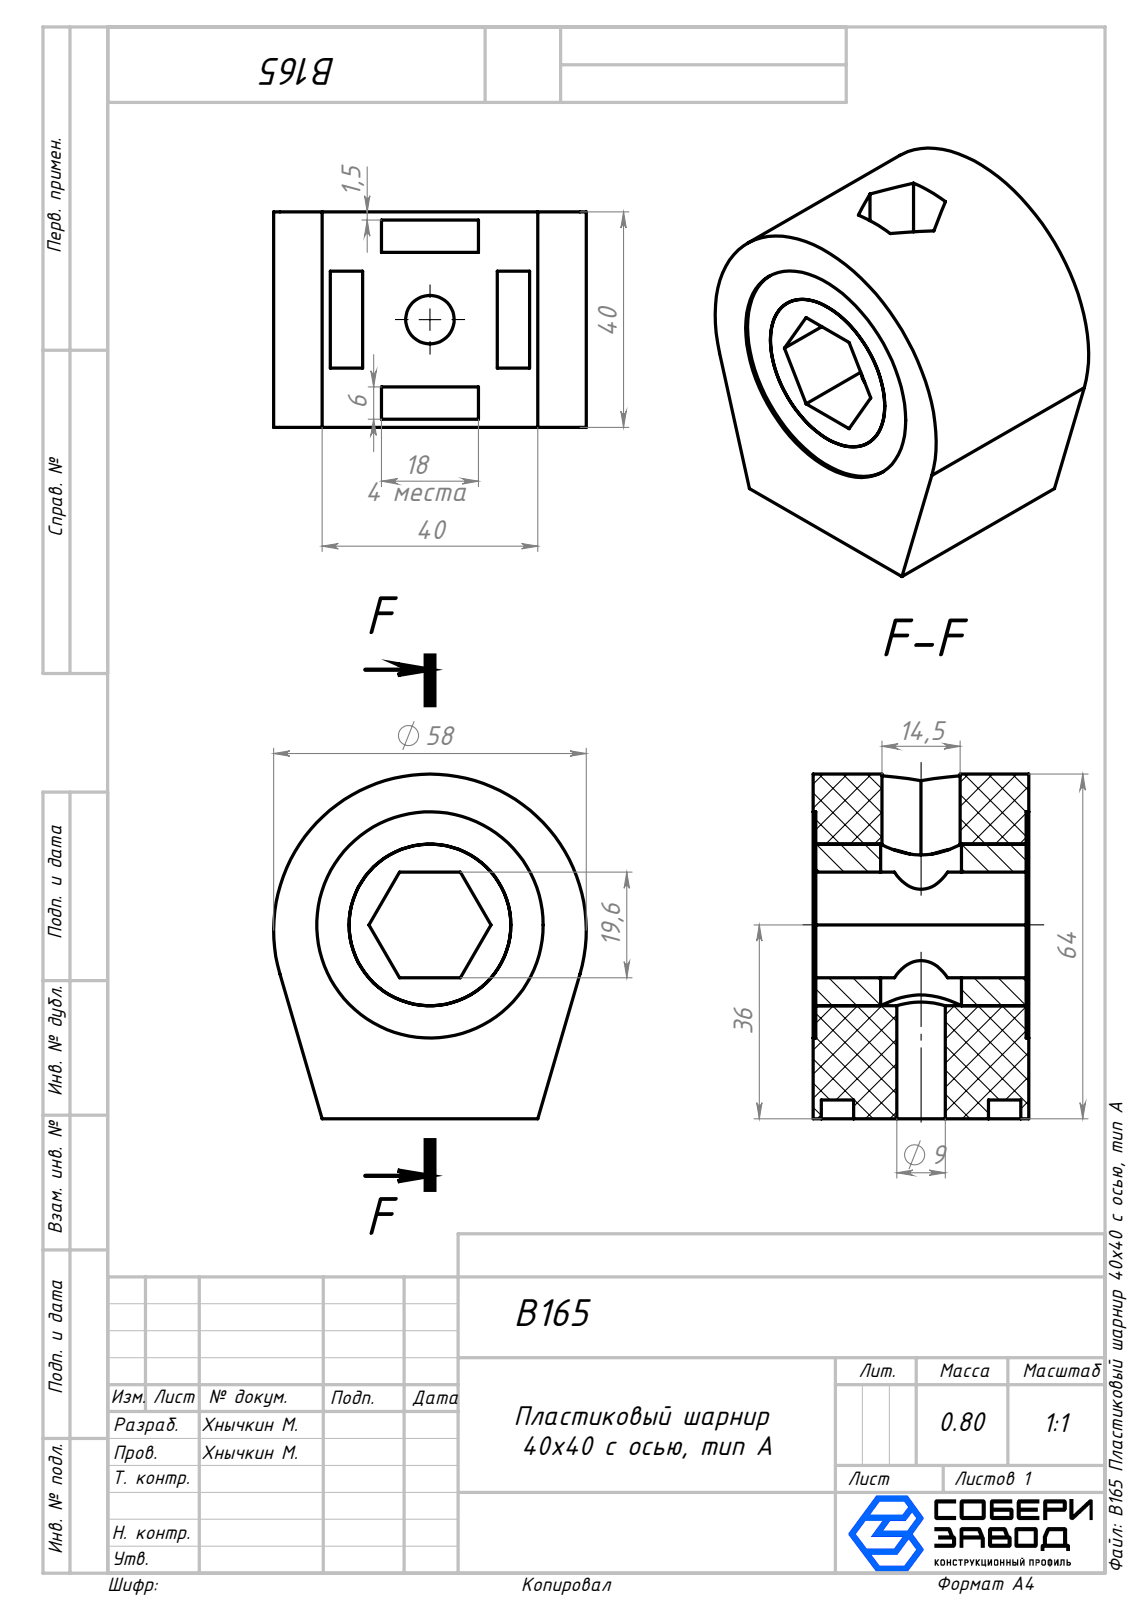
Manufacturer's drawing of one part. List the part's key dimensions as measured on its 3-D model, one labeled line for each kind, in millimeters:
Part name (STEP PRODUCT): B165 Пластиковый шарнир 40х40 с осью, тип А; B165 Цилиндр_00; B165 Пластиковая часть_00
STEP written by: SolidWorks 2026 (AUTOMOTIVE_DESIGN)
Units: millimetres
Bodies: 2 solids, 60 faces (43 planar, 17 cylindrical, 0 other)
Overall size (bounding box): 64 × 58 × 40.5
Volume: 101 880 mm³ · Surface area: 25 087 mm²
Round holes (diameter × count): ⌀9 ×1, ⌀15 ×1, ⌀30 ×1, ⌀42 ×1
Partial cylindrical surfaces — rounded edges, fillets, slot ends (radius × count): R29 ×1
Main face-to-face distances: 0.5, 40, 39.5, 19.6, 39, 3.5, 1, 40.5, 14.5, 6
